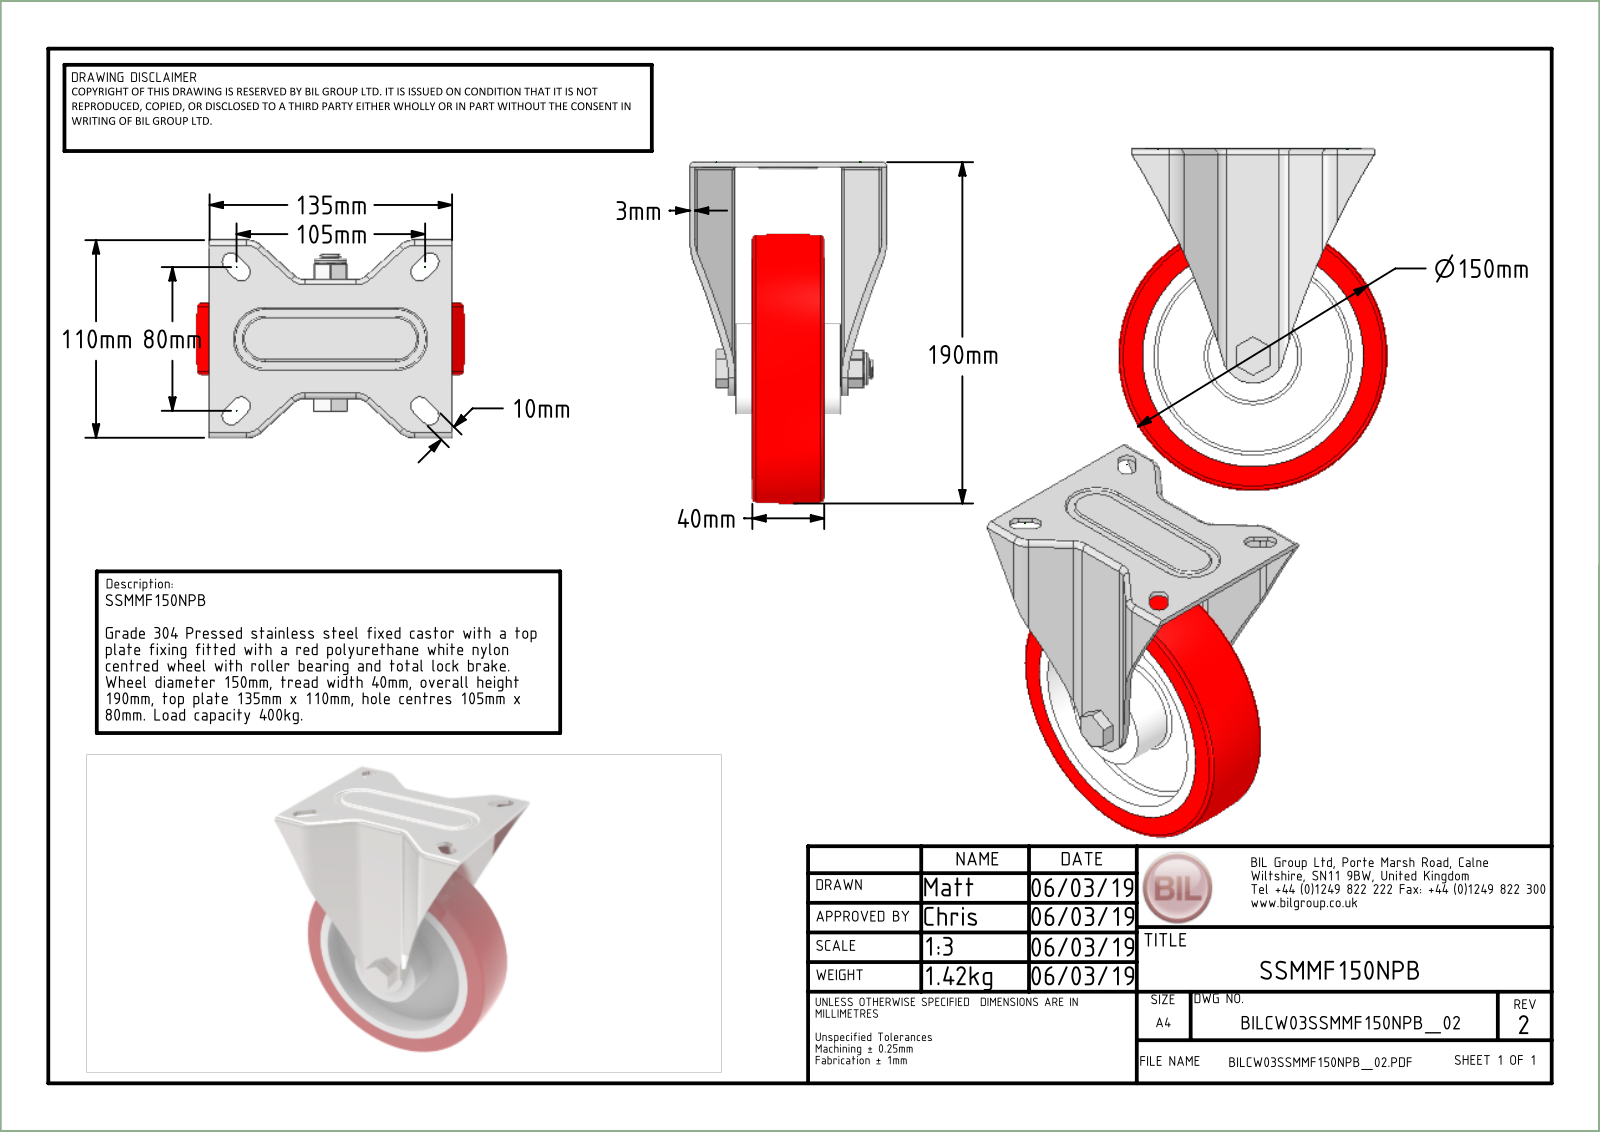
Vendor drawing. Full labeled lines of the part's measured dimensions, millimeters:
Part name (STEP PRODUCT): SSMMF150NPB v3; SSMMF160AS v1; STAINLESS STEEL BRACKET; BZH150WNPRB v1 (+7 more)
STEP written by: Autodesk Translation Framework v13.20.0.188 (AUTOMOTIVE_DESIGN)
Units: millimetres
Bodies: 17 solids, 502 faces (198 planar, 174 cylindrical, 130 other)
Overall size (bounding box): 190 × 150 × 109
Volume: 566 625 mm³ · Surface area: 214 915 mm²
Round holes (diameter × count): ⌀12 ×1, ⌀12.25 ×1, ⌀12.5 ×1, ⌀14 ×1, ⌀20 ×1, ⌀20.5 ×1, ⌀35 ×1, ⌀37 ×1, ⌀122 ×1
Round bosses / shafts (diameter × count): ⌀7.5 ×8, ⌀50 ×1, ⌀34 ×1, ⌀19.9 ×1, ⌀18.5 ×1, ⌀17.5 ×1, ⌀11.83 ×1, ⌀9.84 ×1
Partial cylindrical surfaces — rounded edges, fillets, slot ends (radius × count): R0.5 ×24, R1.5 ×12, R3 ×8, R5.5 ×8, R0.25 ×6, R2 ×4, R6 ×4, R9 ×4
Main face-to-face distances: 2.5, 23, 17, 24.24, 10, 33, 27, 50, 12.5, 29.5
